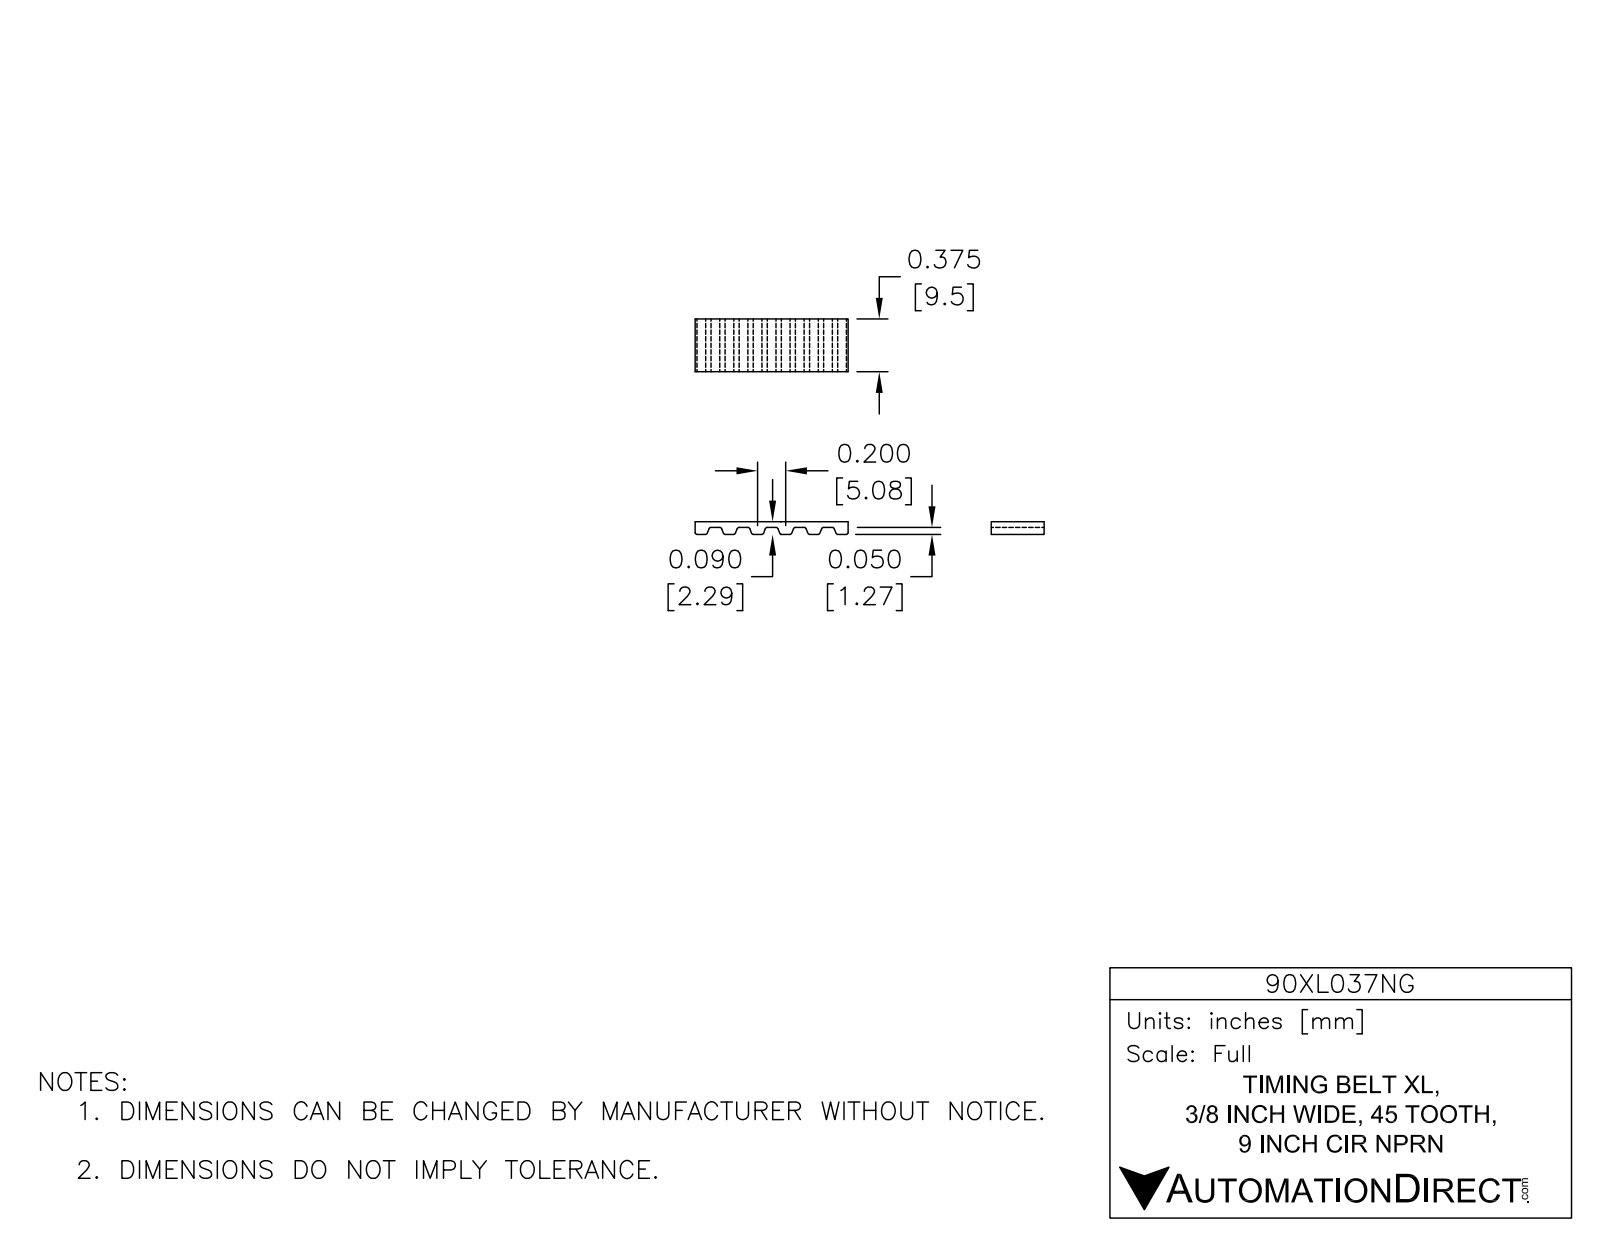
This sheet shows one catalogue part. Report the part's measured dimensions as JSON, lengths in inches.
{"part_name": "90XL037NG", "step_written_by": "SolidWorks 2014 (AUTOMOTIVE_DESIGN)", "units": "inches", "bodies": {"solids": 1, "faces": 388, "planar": 154, "cylindrical": 234, "other": 0}, "overall_size": [3.358, 2, 0.375], "volume_in3": 0.182, "surface_area_in2": 8.557, "partial_cylinders_radius": [[0.015, 180], [0.96, 2], [1, 2]], "face_to_face_distances": [2, 0.04, 1.96, 0.375, 1.92, 0.352, 0.176, 0.528, 0.176, 0.881]}
